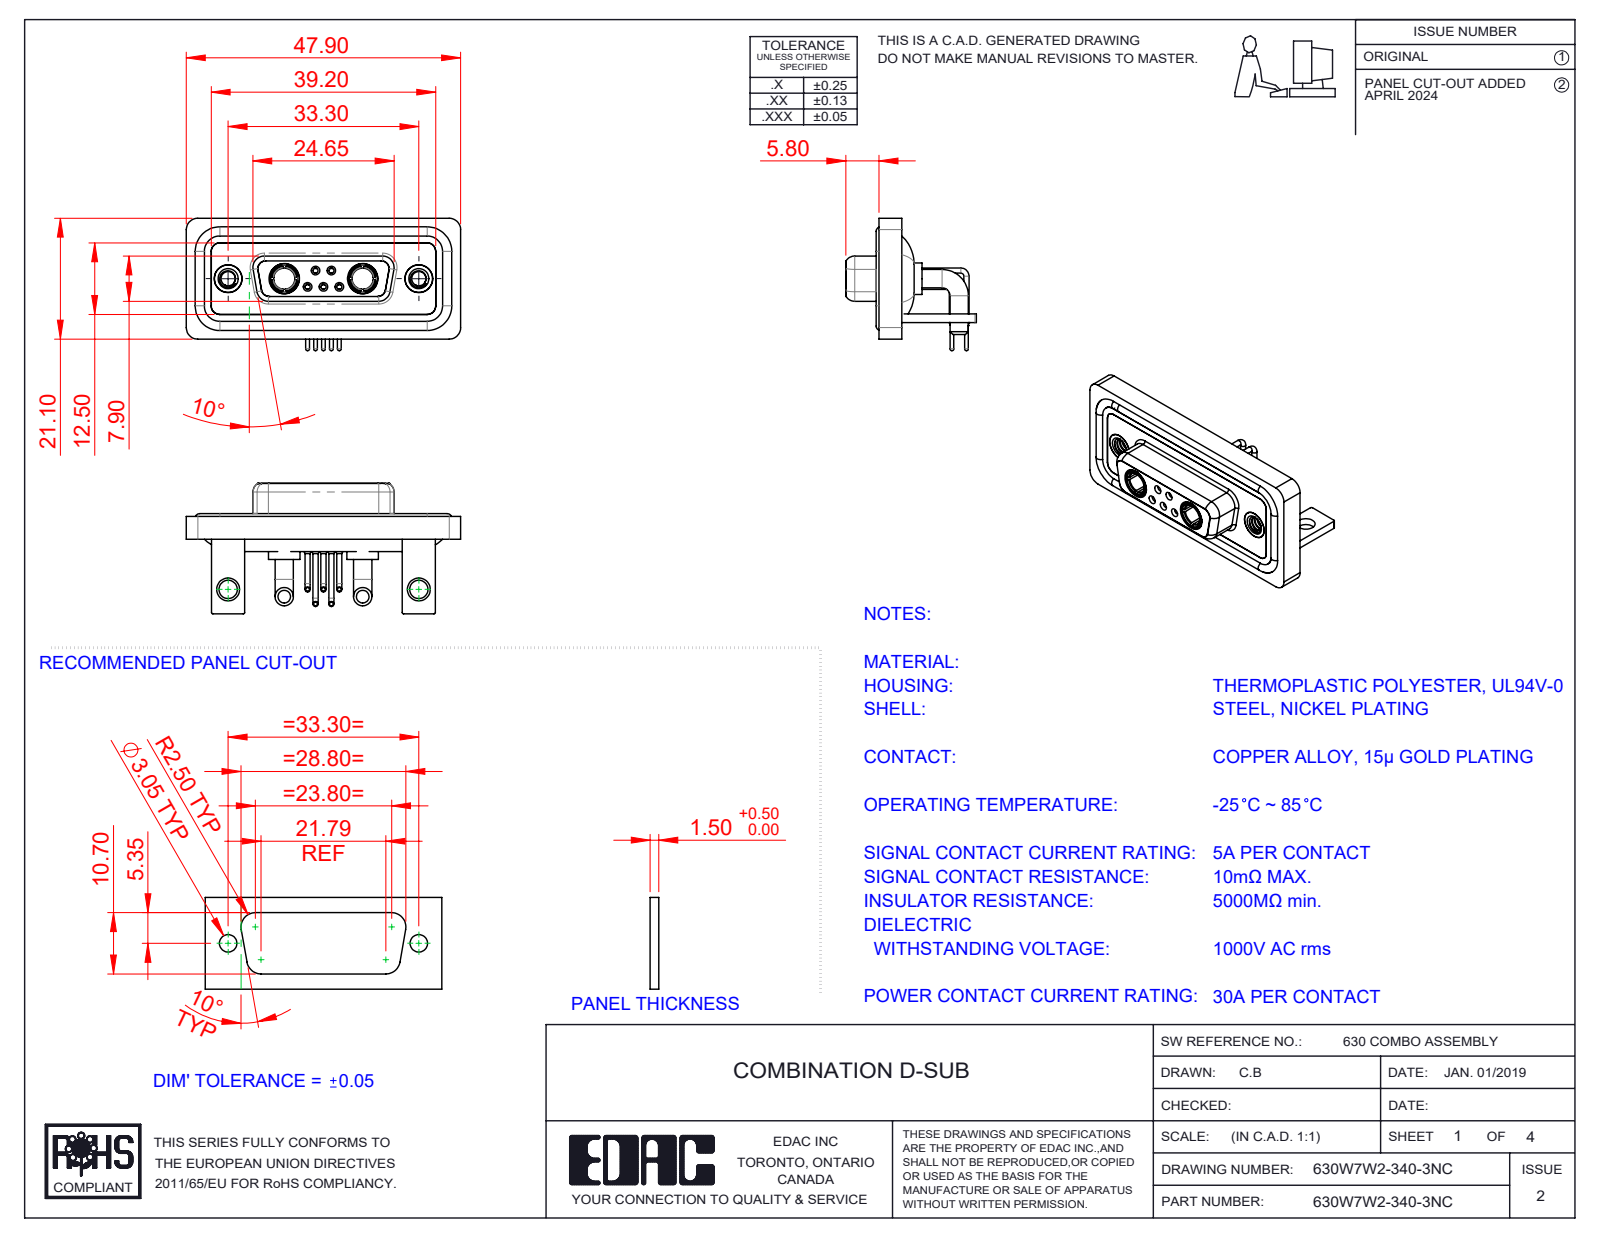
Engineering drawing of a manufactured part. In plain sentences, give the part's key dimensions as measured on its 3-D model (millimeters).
The part is named "630Combo Waterproof Housing_15 Contacts; 630Combo Threaded Rivet_A; 630Combo Housing_7W2; 630Combo Contact Row 2_50 Contacts (+6 more)". Its 3-D file was written by "SolidWorks 2023 (CONFIG_CONTROL_DESIGN)". It is 18 solids with 849 faces: 258 planar, 375 cylindrical and 216 other. Overall it measures 47.9 by 23.12 by 22.8 millimeters. Its volume is 6 612 cubic millimeters and its surface area 10 981 square millimeters. Round holes: 5 of diameter 0.9, 5 of diameter 1.1, 5 of diameter 1.5, 5 of diameter 2, 4 of diameter 4.85, 3 of diameter 1.6, 2 of diameter 1.7, 2 of diameter 2.5, 2 of diameter 3.2, 2 of diameter 3.7, 2 of diameter 4, 2 of diameter 4.05. Round bosses or shafts: 6 of diameter 1.6, 5 of diameter 0.9, 5 of diameter 0.65, 4 of diameter 3.2, 2 of diameter 5.5, 2 of diameter 5.2, 2 of diameter 4.96, 2 of diameter 4.95. Partial cylindrical surfaces (rounded edges, fillets, slot ends): 21 of radius 2, 18 of radius 1.5, 16 of radius 0.25, 12 of radius 1.35, 8 of radius 1.6, 5 of radius 0.5, 4 of radius 0.6, 4 of radius 0.65. The main face-to-face distances are 0.4, 2.9, 1.5, 1.8, 3.7, 1.1, 4.1, 1.6, 2.5, 1.4. The hole center spacings are 3.16, 2.77, 9.8, 23.5, 33.3, 4.31, 4.33, 5.03.
